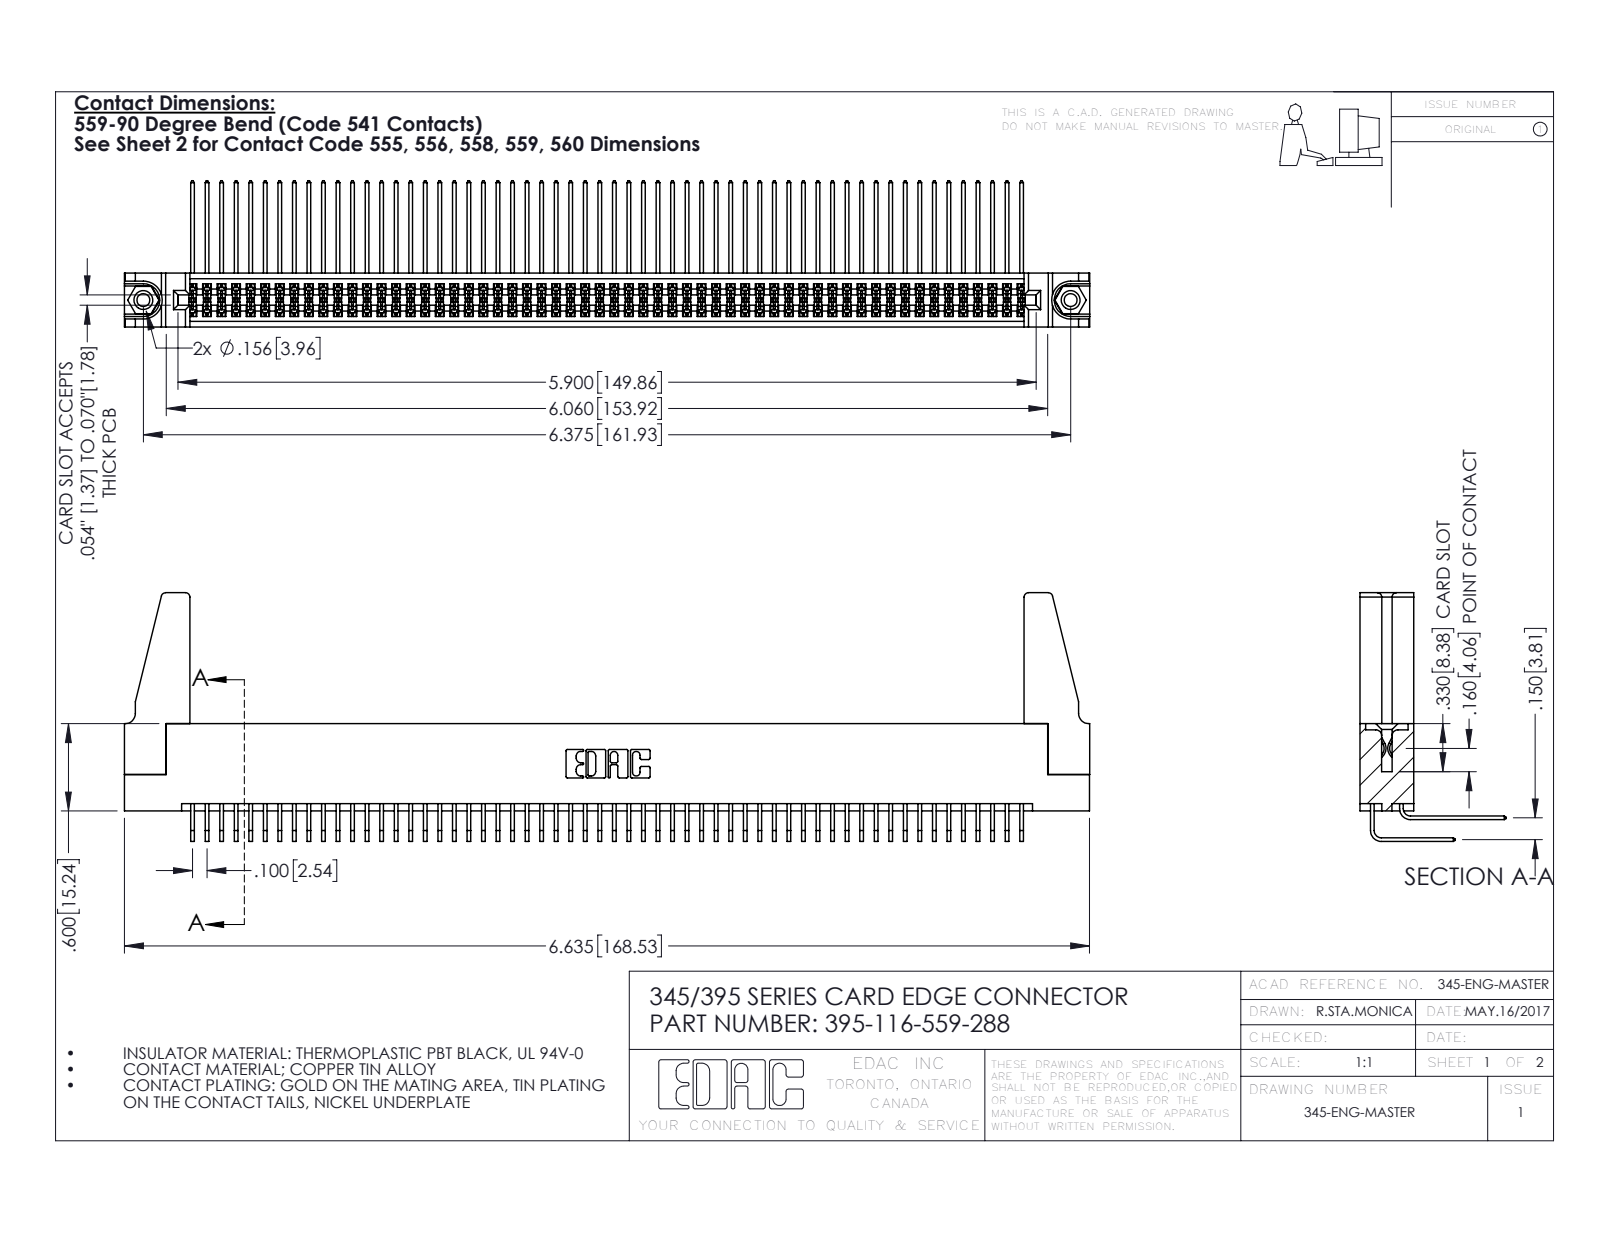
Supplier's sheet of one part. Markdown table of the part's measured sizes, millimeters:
| quantity | value |
| --- | --- |
| part name | 345-292-001_559 Tail - 2; 345-220-078_345-220-088; 345-250-001_345-250-001-102; 395-116-559-288 (+2 more) |
| STEP written by | SolidWorks 2016 (CONFIG_CONTROL_DESIGN) |
| units | millimeters |
| bodies | 121 solids, 6282 faces (4212 planar, 2054 cylindrical, 16 other) |
| overall size | 168.6 × 43.4 × 25.5 |
| volume | 20 450 mm³ |
| surface area | 31 990 mm² |
| round holes (diameter × count) | 2.3 × 2, 3.2 × 2, 4 × 2, 1.6 × 1 |
| round bosses / shafts (diameter × count) | 3.9 × 2 |
| partial cylindrical surfaces (radius × count) | 0.2 × 174, 0.3 × 22, 0.8 × 8, 0.2 × 6, 0.8 × 6, 0.7 × 3, 0.4 × 2, 0.5 × 2 |
| main face-to-face distances | 1.8, 7.6, 9.4, 5.1, 2.5, 6.9, 0.6, 5.7, 4.4, 3.8 |
| hole center spacings | 6.9, 155.9, 161.9 |
